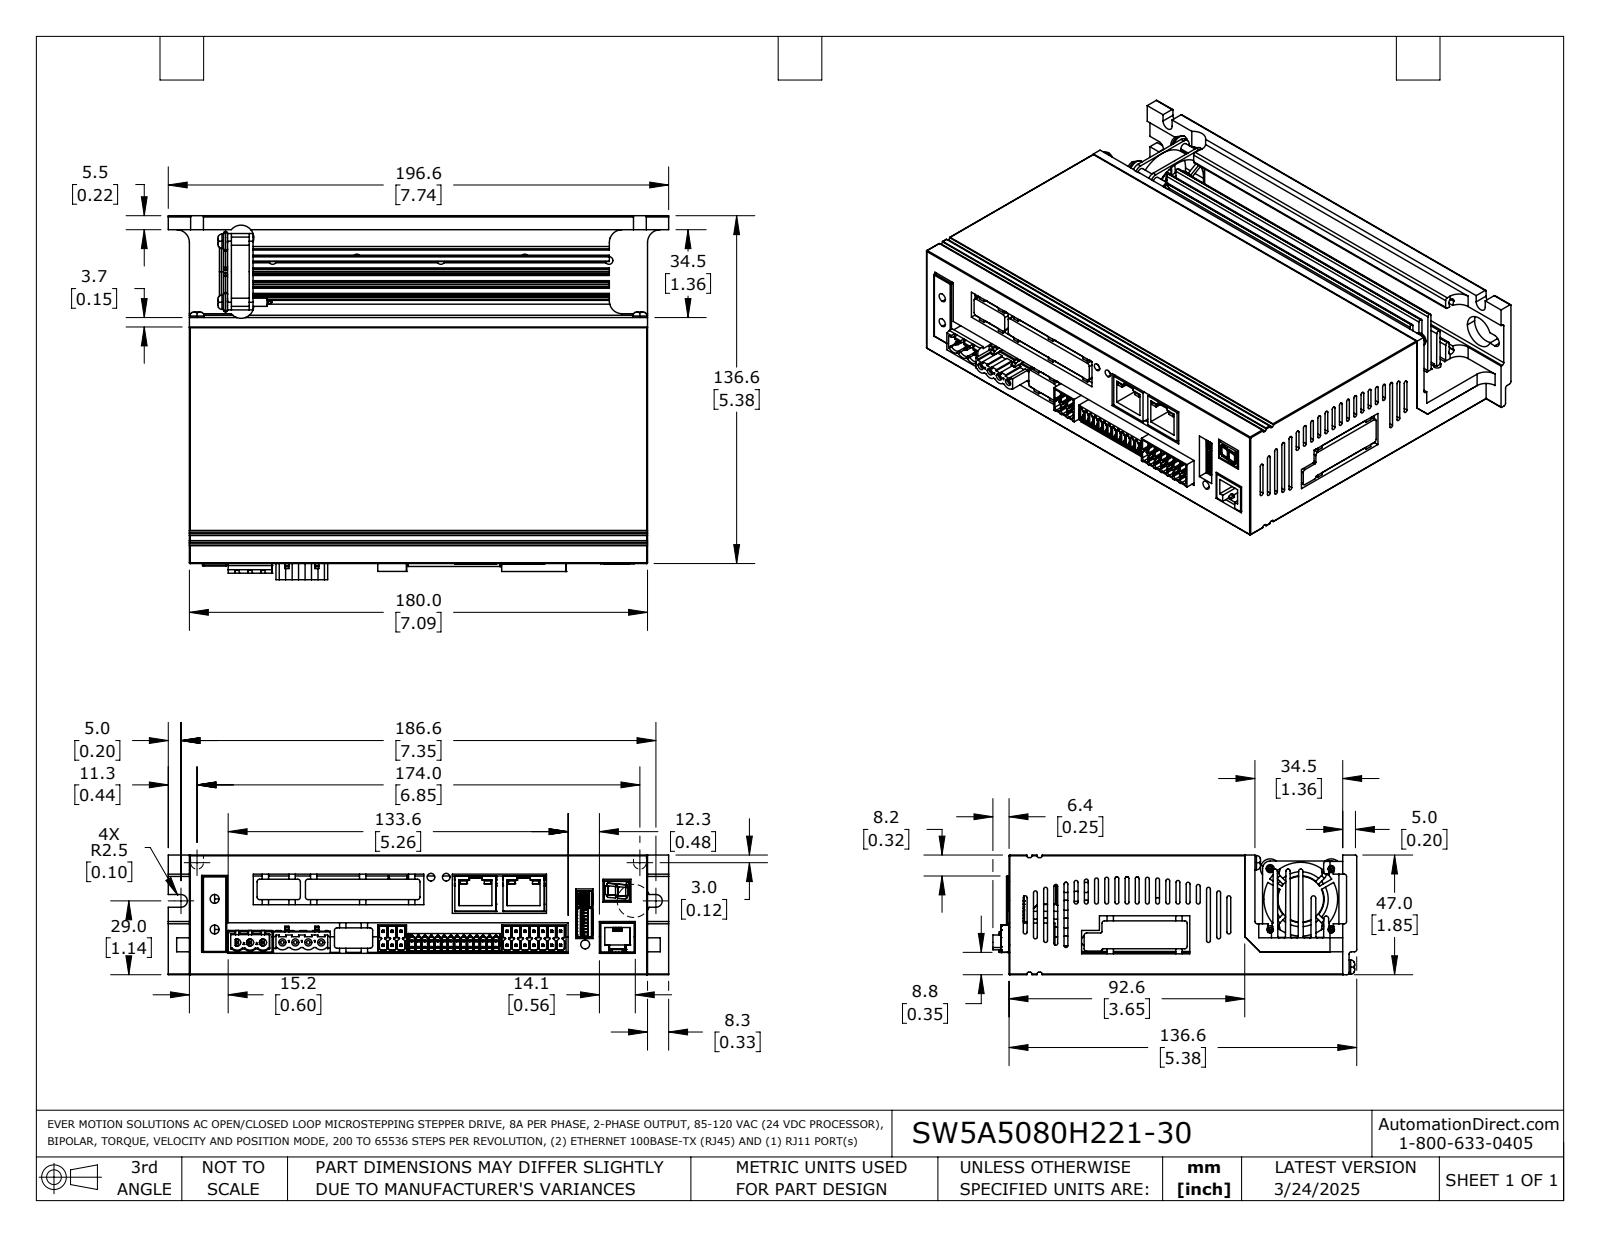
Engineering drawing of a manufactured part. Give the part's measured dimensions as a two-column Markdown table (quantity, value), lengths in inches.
| quantity | value |
| --- | --- |
| part name | SW5A5080H221-30C0680 |
| STEP written by | SolidWorks 2024 (AUTOMOTIVE_DESIGN) |
| units | inches |
| bodies | 33 solids, 6114 faces (3815 planar, 1884 cylindrical, 415 other) |
| overall size | 7.74 × 5.628 × 1.85 |
| volume | 20.95 in³ |
| surface area | 486.3 in² |
| round holes (diameter × count) | 0.04 × 80, 0.055 × 24, 0.126 × 22, 0.035 × 20, 0.039 × 20, 0.157 × 17, 0.035 × 16, 0.06 × 13, 0.012 × 12, 0.047 × 12, 0.118 × 12, 0.03 × 10 |
| round bosses / shafts (diameter × count) | 0.22 × 8, 0.083 × 6, 0.055 × 3, 0.11 × 2, 0.063 × 2, 1.181 × 1, 0.709 × 1, 0.018 × 1 |
| partial cylindrical surfaces (radius × count) | 0.004 × 192, 0.012 × 91, 0.008 × 84, 0.03 × 56, 0.035 × 31, 0.02 × 19, 0.039 × 17, 0.006 × 12 |
| main face-to-face distances | 0.079, 1.772, 0.063, 0.345, 0.282, 0.267, 0.204, 0.197, 1.244, 1.505 |
| hole center spacings | 0.206, 0.416, 0.112, 0.1, 0.091, 0.276, 0.047, 0.128 |
